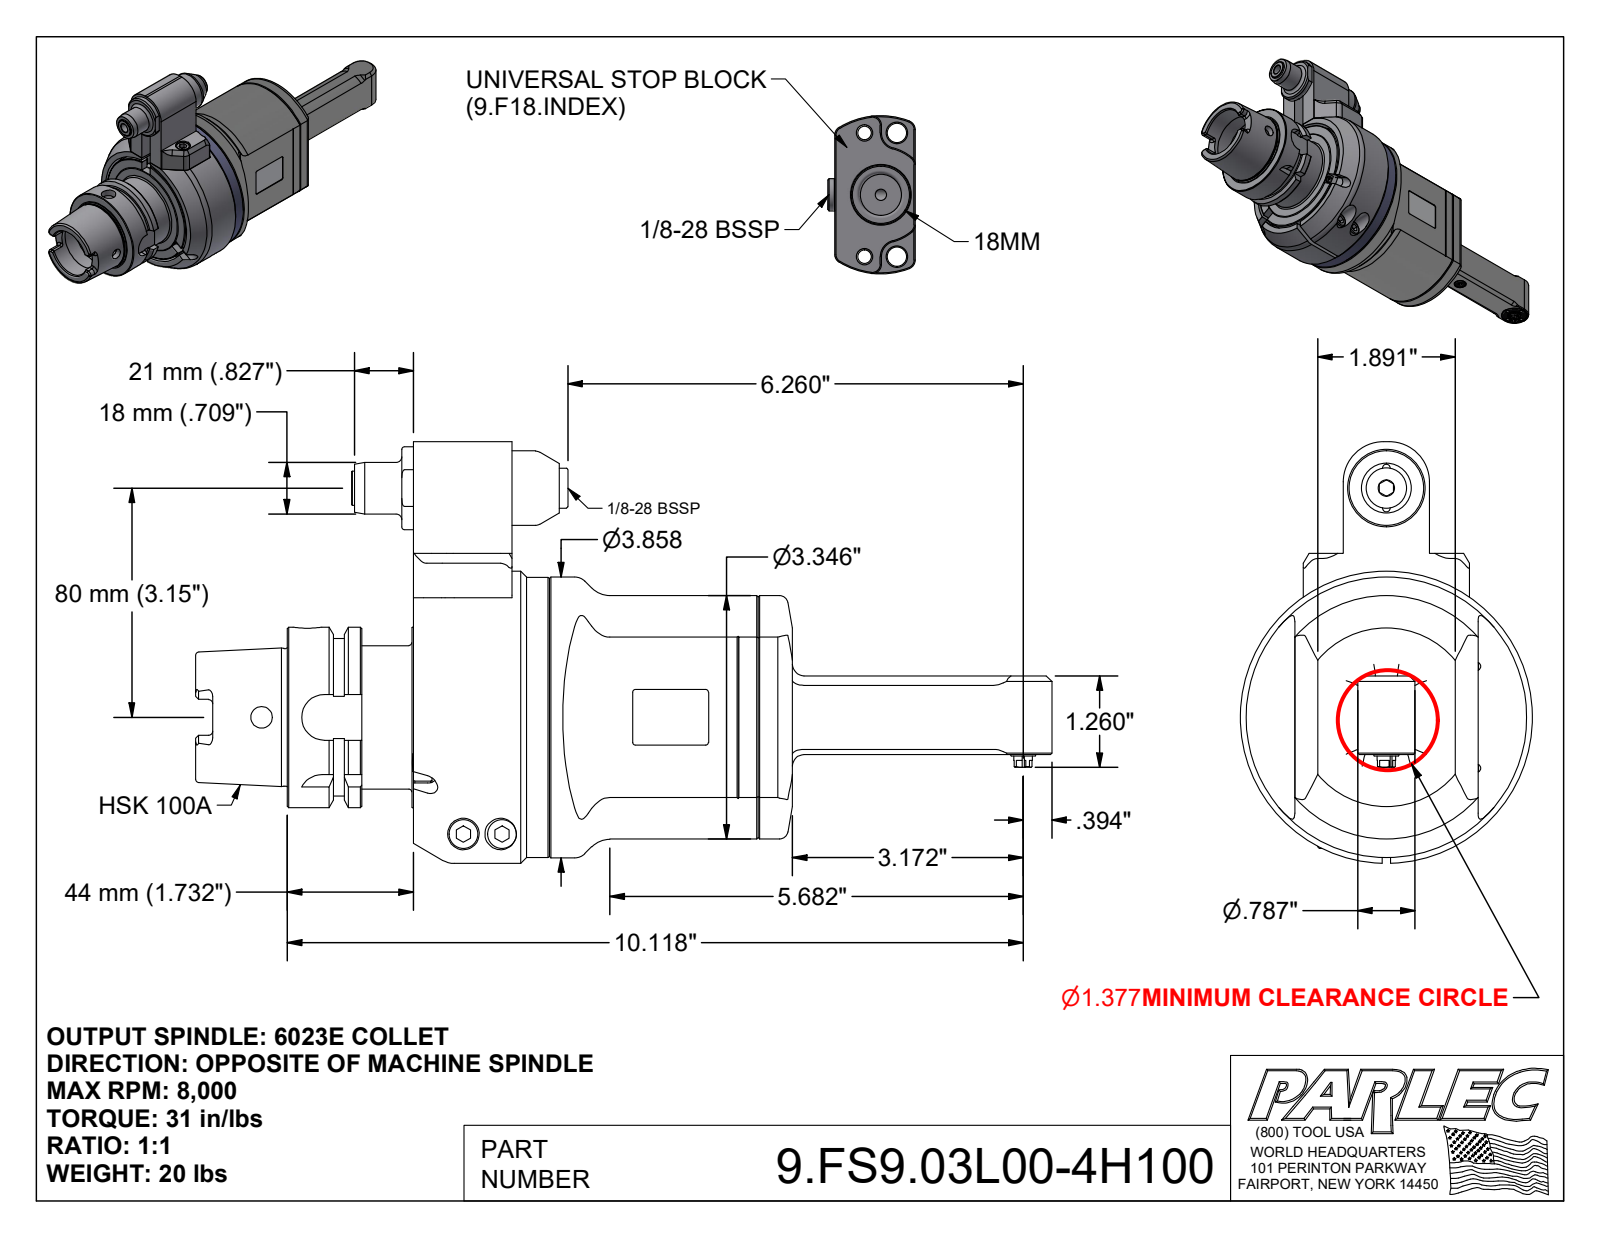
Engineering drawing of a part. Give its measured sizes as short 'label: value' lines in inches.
name: 9.FS9.03L00-4H100; 9_GA1_568_2; 9_FS9_03L00
written by: Autodesk Inventor 2022 (AUTOMOTIVE_DESIGN)
unit: in
bodies: 5 solids, 573 faces (282 planar, 145 cylindrical, 146 other)
size: 11.772 × 5.796 × 4.016
volume: 62.75 in³; area: 233.1 in²
holes: 6× ⌀0.102, 2× ⌀0.118, 2× ⌀0.165, 2× ⌀0.197, 2× ⌀0.335, 2× ⌀0.409, 2× ⌀0.433, 2× ⌀0.492, 1× ⌀0.098, 1× ⌀0.256, 1× ⌀0.276, 1× ⌀0.295
bosses: 4× ⌀0.394, 4× ⌀0.236, 3× ⌀0.315, 2× ⌀0.709, 2× ⌀0.098, 1× ⌀4.016, 1× ⌀3.858, 1× ⌀3.85
rounds: 10× R0.157, 8× R0.079, 6× R0.039, 6× R0.059, 4× R0.113, 4× R0.315, 2× R0.02, 2× R0.138
face distances: 1.378, 0.197, 0.098, 0.276, 1.654, 0.984, 0.866, 0.335, 1.083, 1.555
hole spacings: 0.266, 0.376, 0.276, 0.531, 2.125, 4.557, 9.846, 0.512
